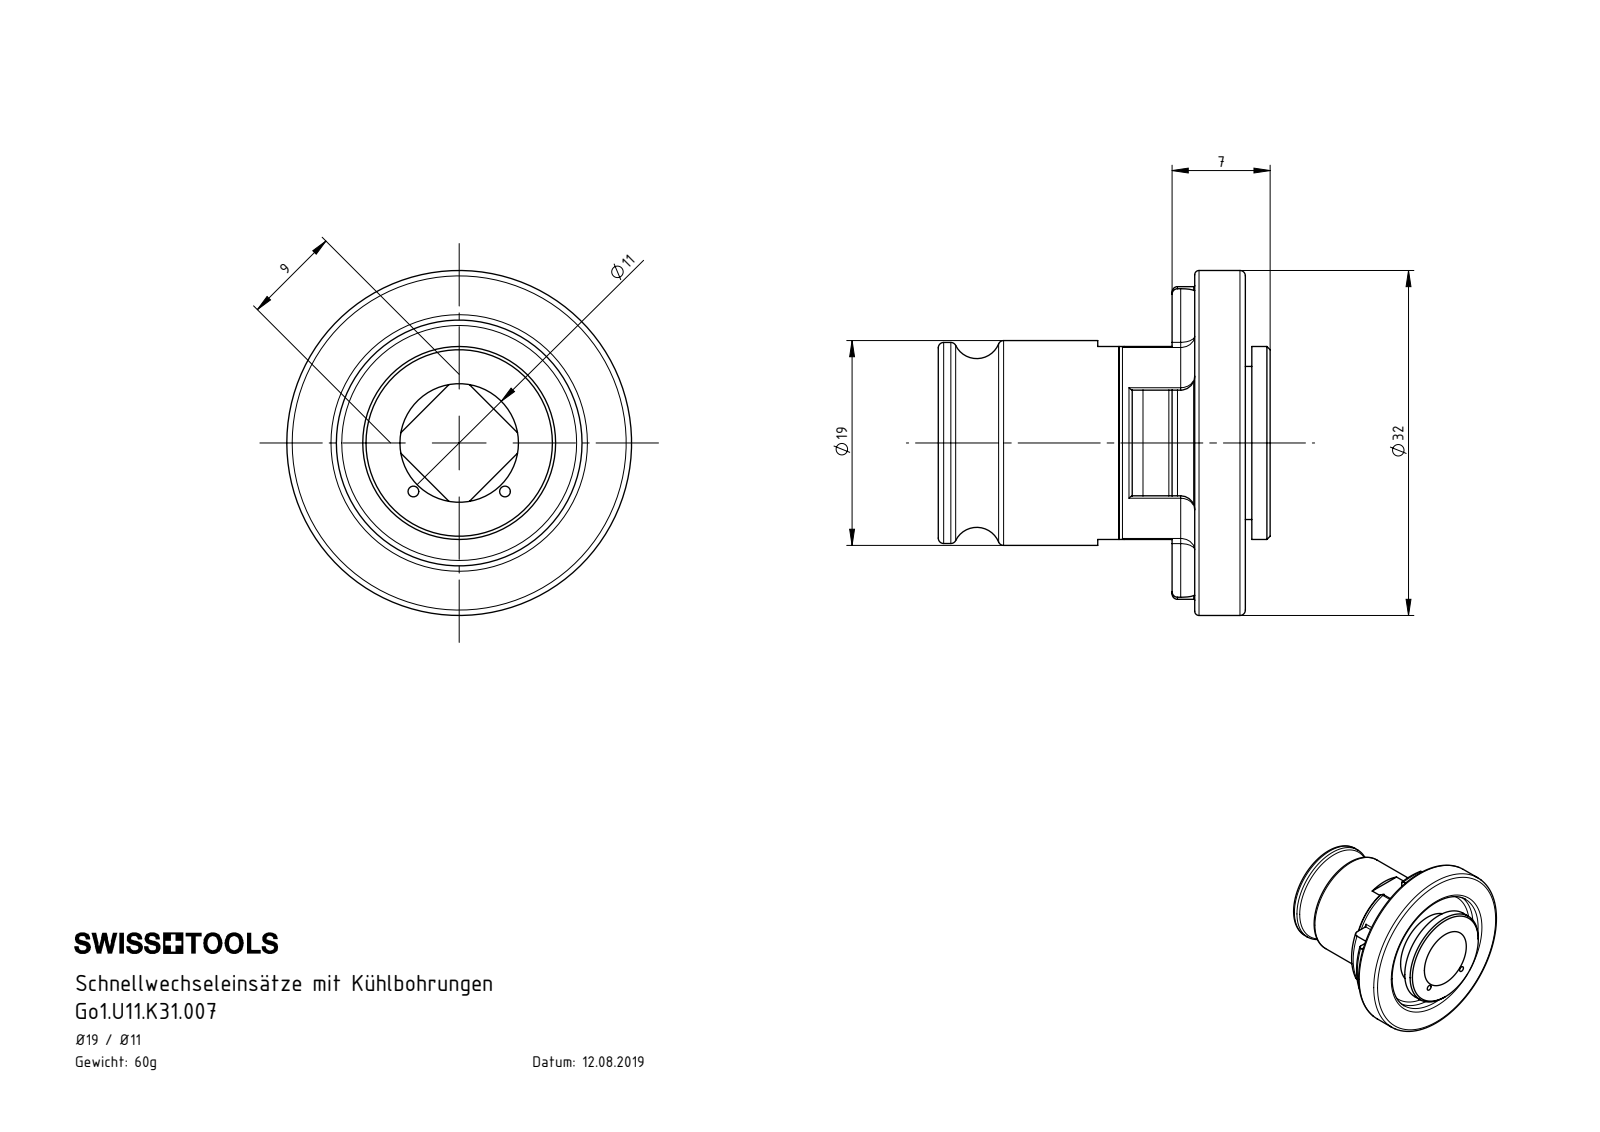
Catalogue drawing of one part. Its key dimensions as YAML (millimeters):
part_name: "Go1.U11.K31.007"
step_written_by: "SolidWorks 2017 (AUTOMOTIVE_DESIGN)"
units: millimeters
bodies: {solids: 1, faces: 126, planar: 36, cylindrical: 37, other: 53}
overall_size: [32, 32, 30.8]
volume: 7693
surface_area: 5151
round_holes:
  - {diameter: 1, count: 2}
  - {diameter: 11, count: 1}
  - {diameter: 11.4, count: 1}
  - {diameter: 22.8, count: 1}
round_bosses_or_shafts:
  - {diameter: 32, count: 1}
  - {diameter: 19, count: 1}
  - {diameter: 18.65, count: 1}
  - {diameter: 18.52, count: 1}
  - {diameter: 17.9, count: 1}
  - {diameter: 14.2, count: 1}
partial_cylinders:
  - {radius: 0.5, count: 8}
  - {radius: 1.3, count: 4}
  - {radius: 12.4, count: 1}
  - {radius: 14.5, count: 1}
face_to_face_distances: [2.35, 4.7, 7, 4.65, 2.3, 9, 23.8, 26.15, 28.5, 30.8]
hole_center_spacings: [6.19, 8.5]
